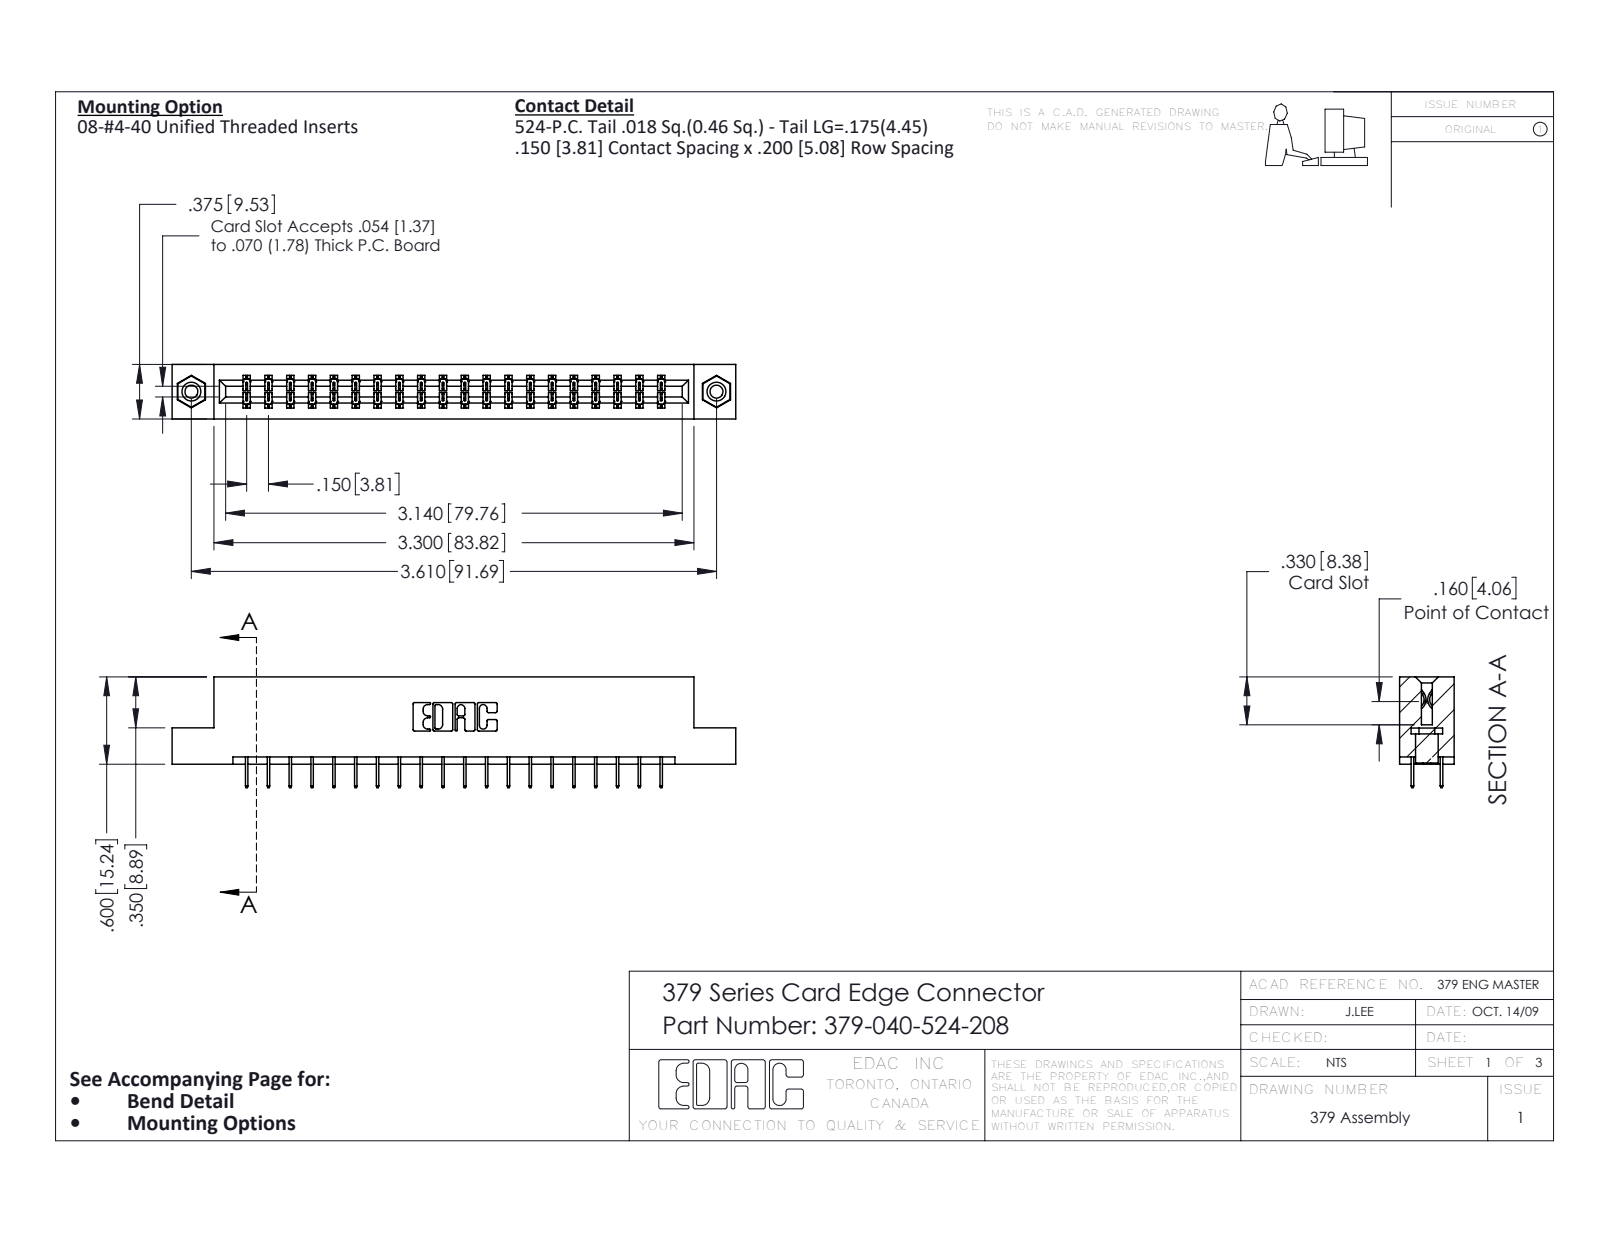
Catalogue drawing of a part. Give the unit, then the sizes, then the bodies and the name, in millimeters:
Units: millimetres
Overall size (bounding box): 98.4 × 19.4 × 9.5
Round holes (diameter × count): ⌀2.3 ×2, ⌀3.2 ×2, ⌀4 ×2
Round bosses / shafts (diameter × count): ⌀3.9 ×2
Partial cylindrical surfaces — rounded edges, fillets, slot ends (radius × count): R0.2 ×60, R0.3 ×22, R0.2 ×6, R0.8 ×6, R0.7 ×3, R0.4 ×2, R0.6 ×2, R0.6 ×2
Main face-to-face distances: 7.6, 9.5, 1.9, 5.1, 2.5, 5.7, 3.8, 1.3, 15.2, 14
Hole centre spacings: 91.7
Volume: 10 100 mm³ · Surface area: 11 030 mm²
Bodies: 43 solids, 2414 faces (1782 planar, 616 cylindrical, 16 other)
Part name (STEP PRODUCT): 379 Part_Flush - .156 Dia - TI; 345-292-001_345-293-124; 345-250-001_345-250-003-102; 379-040-524-208
STEP written by: SolidWorks 2016 (CONFIG_CONTROL_DESIGN)
